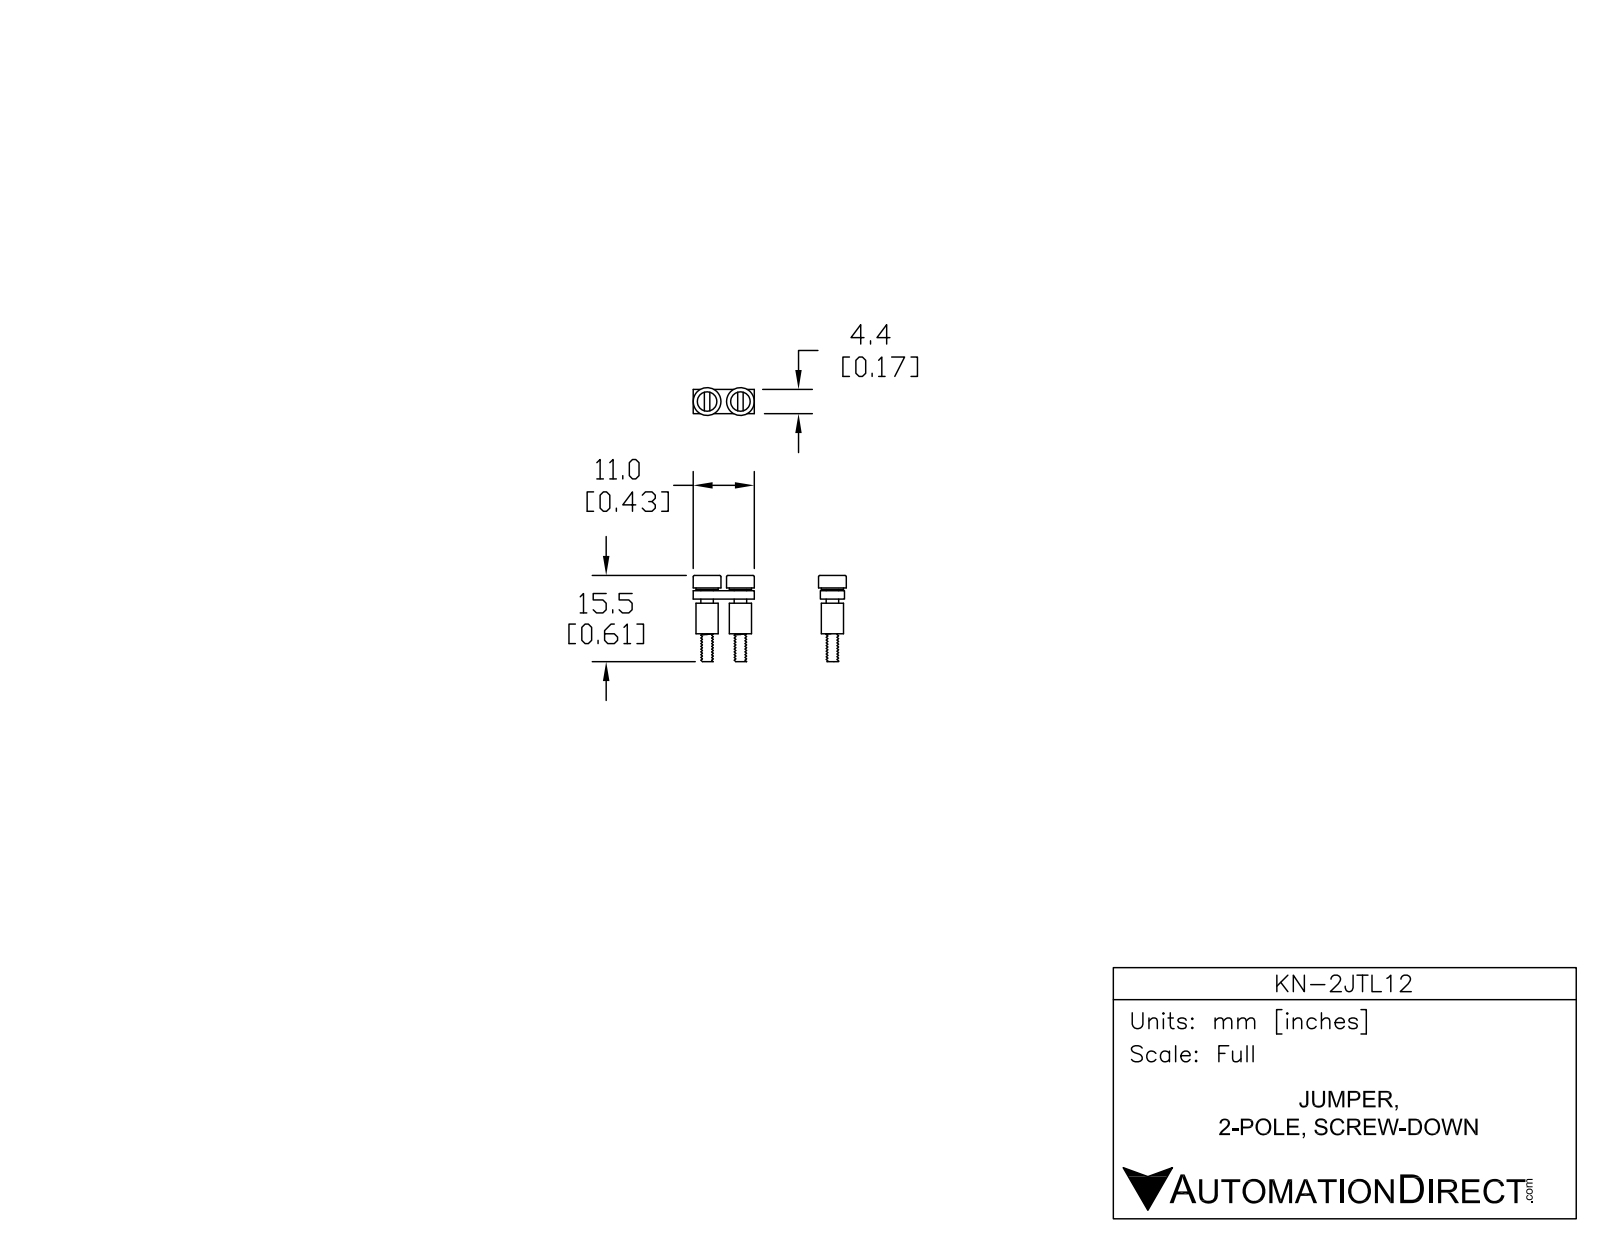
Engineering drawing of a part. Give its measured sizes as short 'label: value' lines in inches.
name: KN-2JTL12
written by: SolidWorks 2014 (AUTOMOTIVE_DESIGN)
unit: in
bodies: 7 solids, 70 faces (32 planar, 26 cylindrical, 12 other)
size: 0.61 × 0.433 × 0.197
volume: 0.019 in³; area: 1.36 in²
holes: 2× ⌀0.118, 2× ⌀0.138
bosses: 2× ⌀0.197, 2× ⌀0.157, 2× ⌀0.089
face distances: 0.059, 0.079, 0.089, 0.069, 0.02, 0.108, 0.098, 0.039, 0.197, 0.03
hole spacings: 0.236
